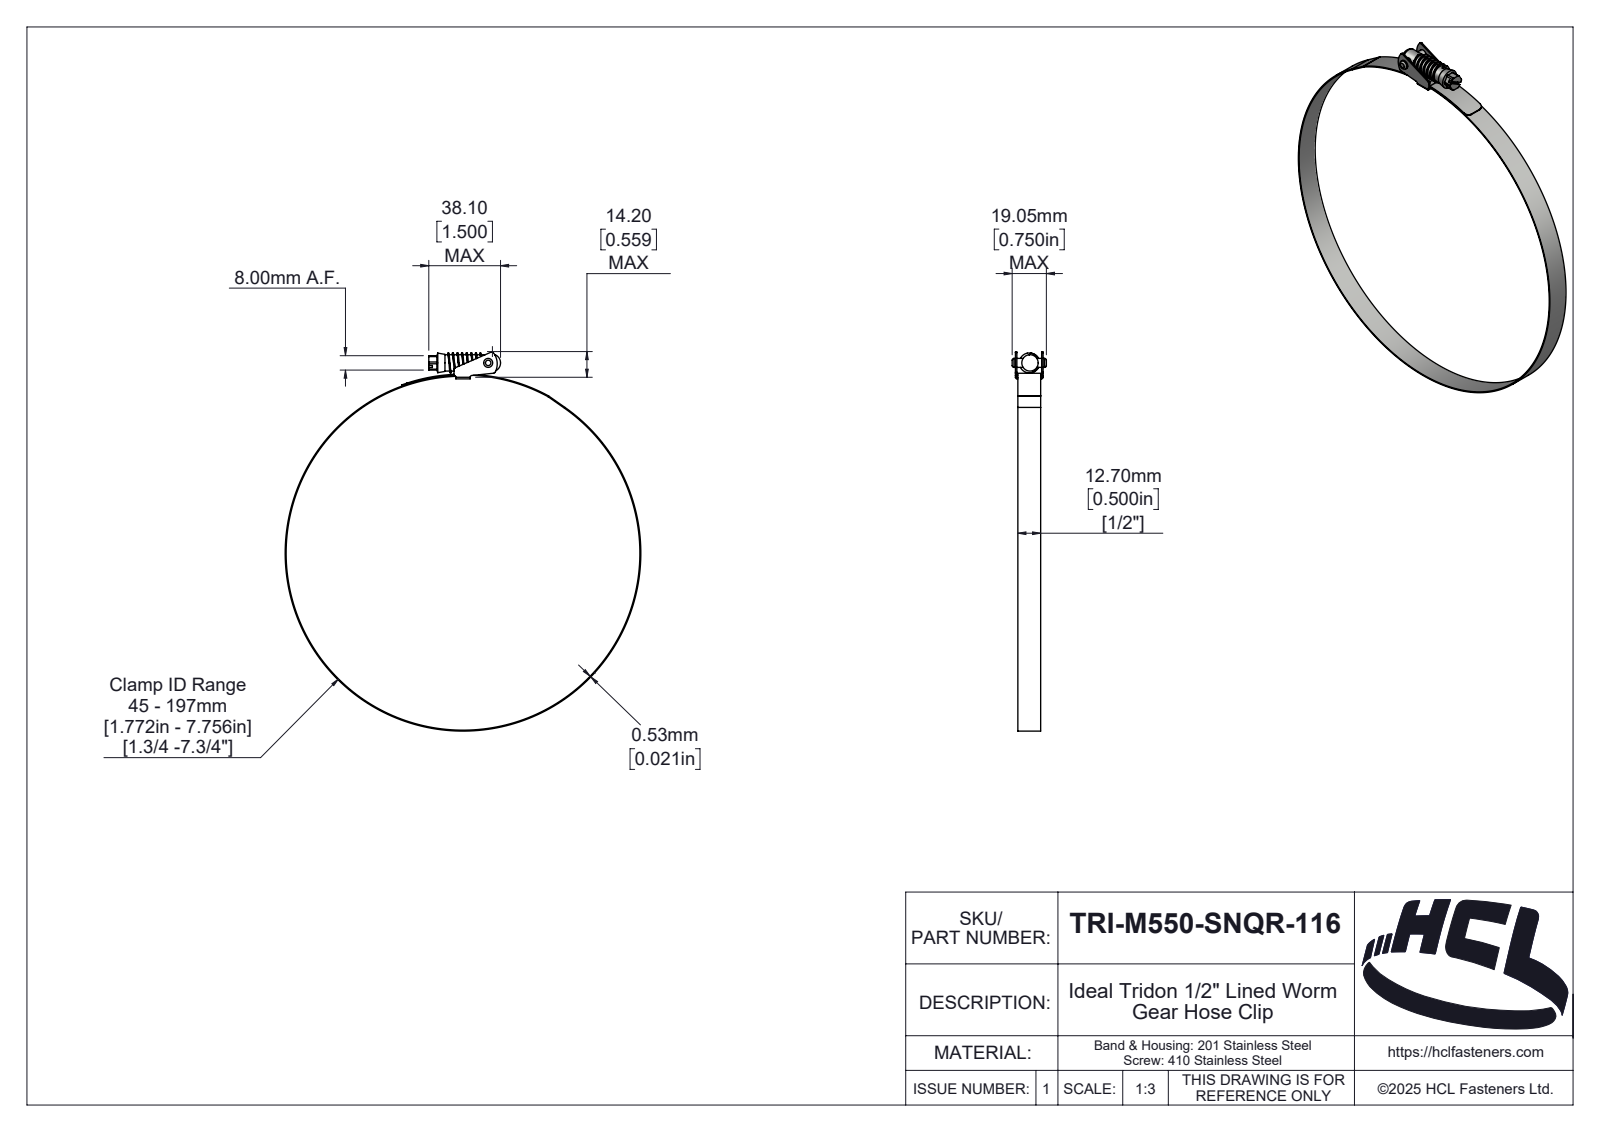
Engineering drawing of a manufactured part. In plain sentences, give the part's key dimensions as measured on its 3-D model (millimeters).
The part is named "TRI-M550-SNQR-116". Its 3-D file was written by "SolidWorks 2025 (AUTOMOTIVE_DESIGN)". It is 5 solids with 222 faces: 44 planar, 112 cylindrical and 66 other. Overall it measures 211.02 by 198.06 by 19.05 millimeters. Its volume is 7 591 cubic millimeters and its surface area 20 929 square millimeters. Round holes: 1 of diameter 5, 1 of diameter 197. Round bosses or shafts: 1 of diameter 198.06, 1 of diameter 9.1. Partial cylindrical surfaces (rounded edges, fillets, slot ends): 11 of radius 1, 2 of radius 0.1, 2 of radius 0.9, 2 of radius 3, 1 of radius 0.46, 1 of radius 1.89, 1 of radius 2, 1 of radius 2.35. The main face-to-face distances are 0.8, 1.35, 14.05, 14.6, 0.55, 13.25, 12.7, 15.4, 13.8, 0.53. The hole center spacings are 106.82.
